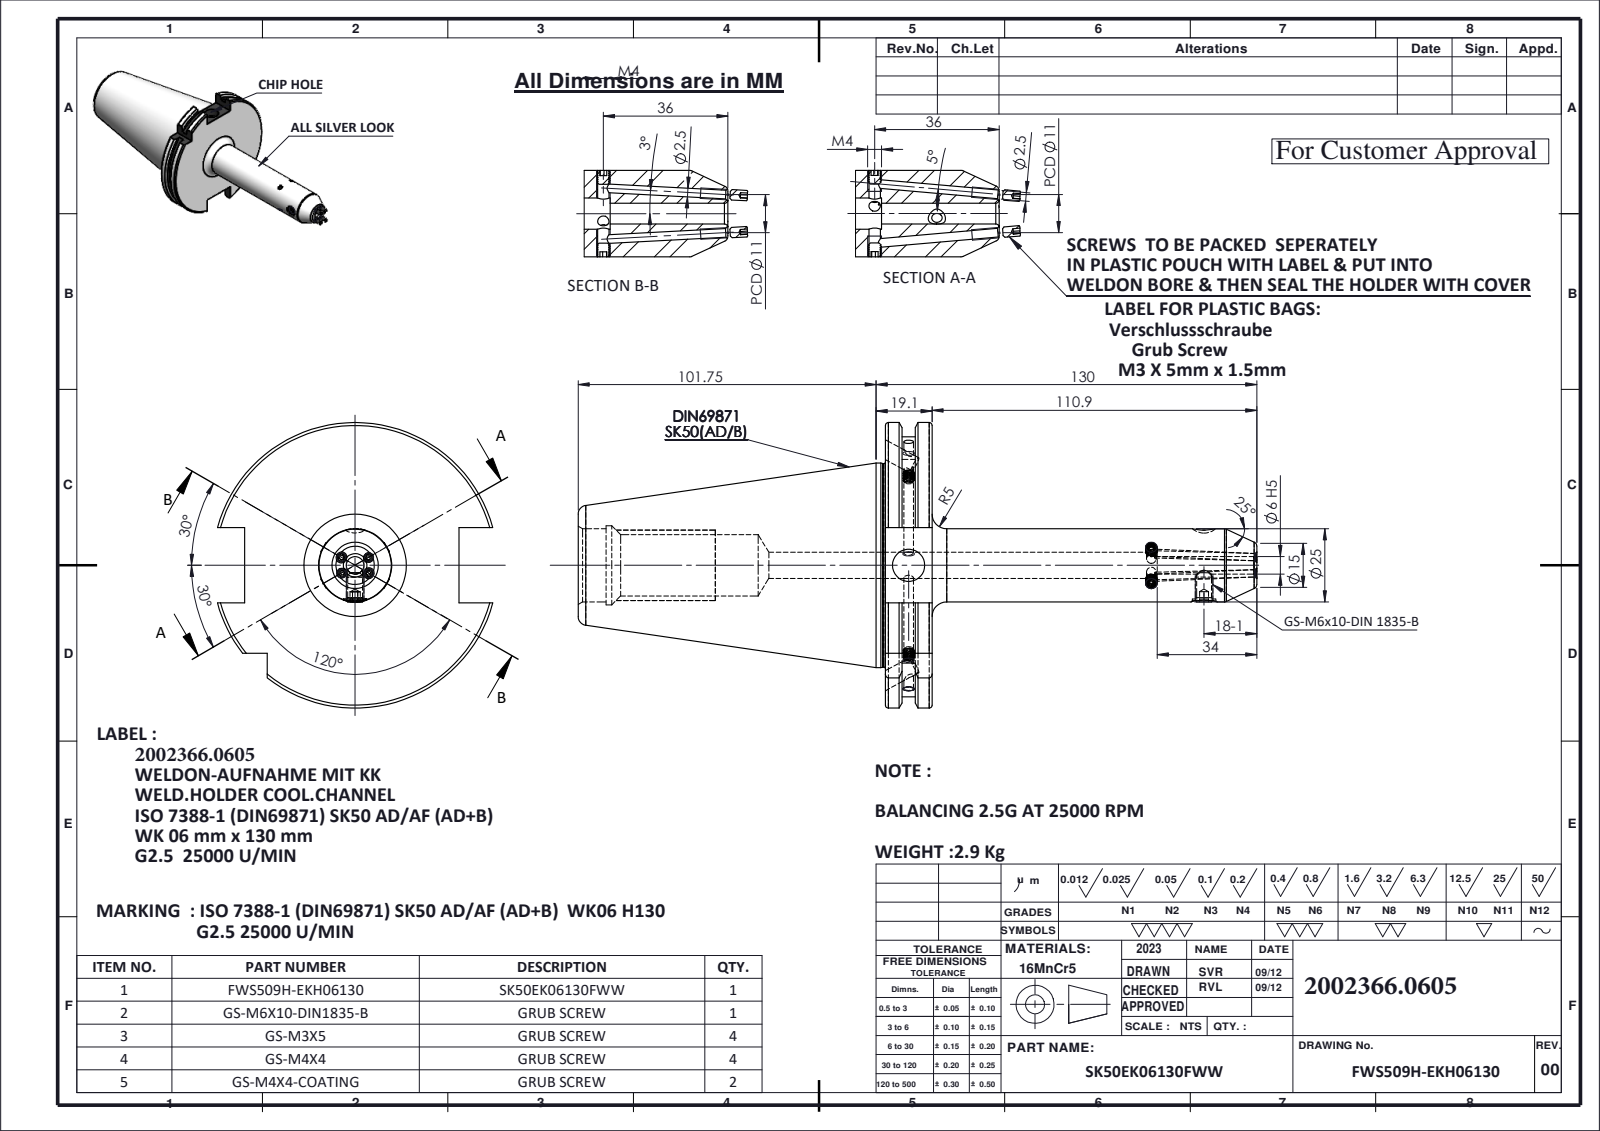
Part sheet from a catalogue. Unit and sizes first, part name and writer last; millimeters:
Units: millimetres
Overall size (bounding box): 237.88 × 97.5 × 94.05
Round holes (diameter × count): ⌀2.5 ×4, ⌀3.3 ×4, ⌀6 ×3, ⌀5 ×1, ⌀8 ×1, ⌀9 ×1, ⌀11 ×1, ⌀21 ×1, ⌀25 ×1, ⌀27 ×1
Round bosses / shafts (diameter × count): ⌀4 ×6, ⌀3 ×4, ⌀69.85 ×1, ⌀69.45 ×1, ⌀6 ×1
Partial cylindrical surfaces — rounded edges, fillets, slot ends (radius × count): R44.9 ×1, R48.75 ×1
Main face-to-face distances: 15.9, 5.66, 10.24, 10.14, 4.48, 5.76, 104.95, 110.61, 115.09, 120.85
Volume: 380 431 mm³ · Surface area: 56 798 mm²
Bodies: 12 solids, 539 faces (152 planar, 133 cylindrical, 254 other)
Part name (STEP PRODUCT): SK50EK06130FWW; GS-M4X4_DIN 913 - M4 x 4-N; FWS509H-EKH06130; GS-M4X4-COATING_DIN 913 - M4 x 4-N (+2 more)
STEP written by: SolidWorks 2023 (CONFIG_CONTROL_DESIGN)
